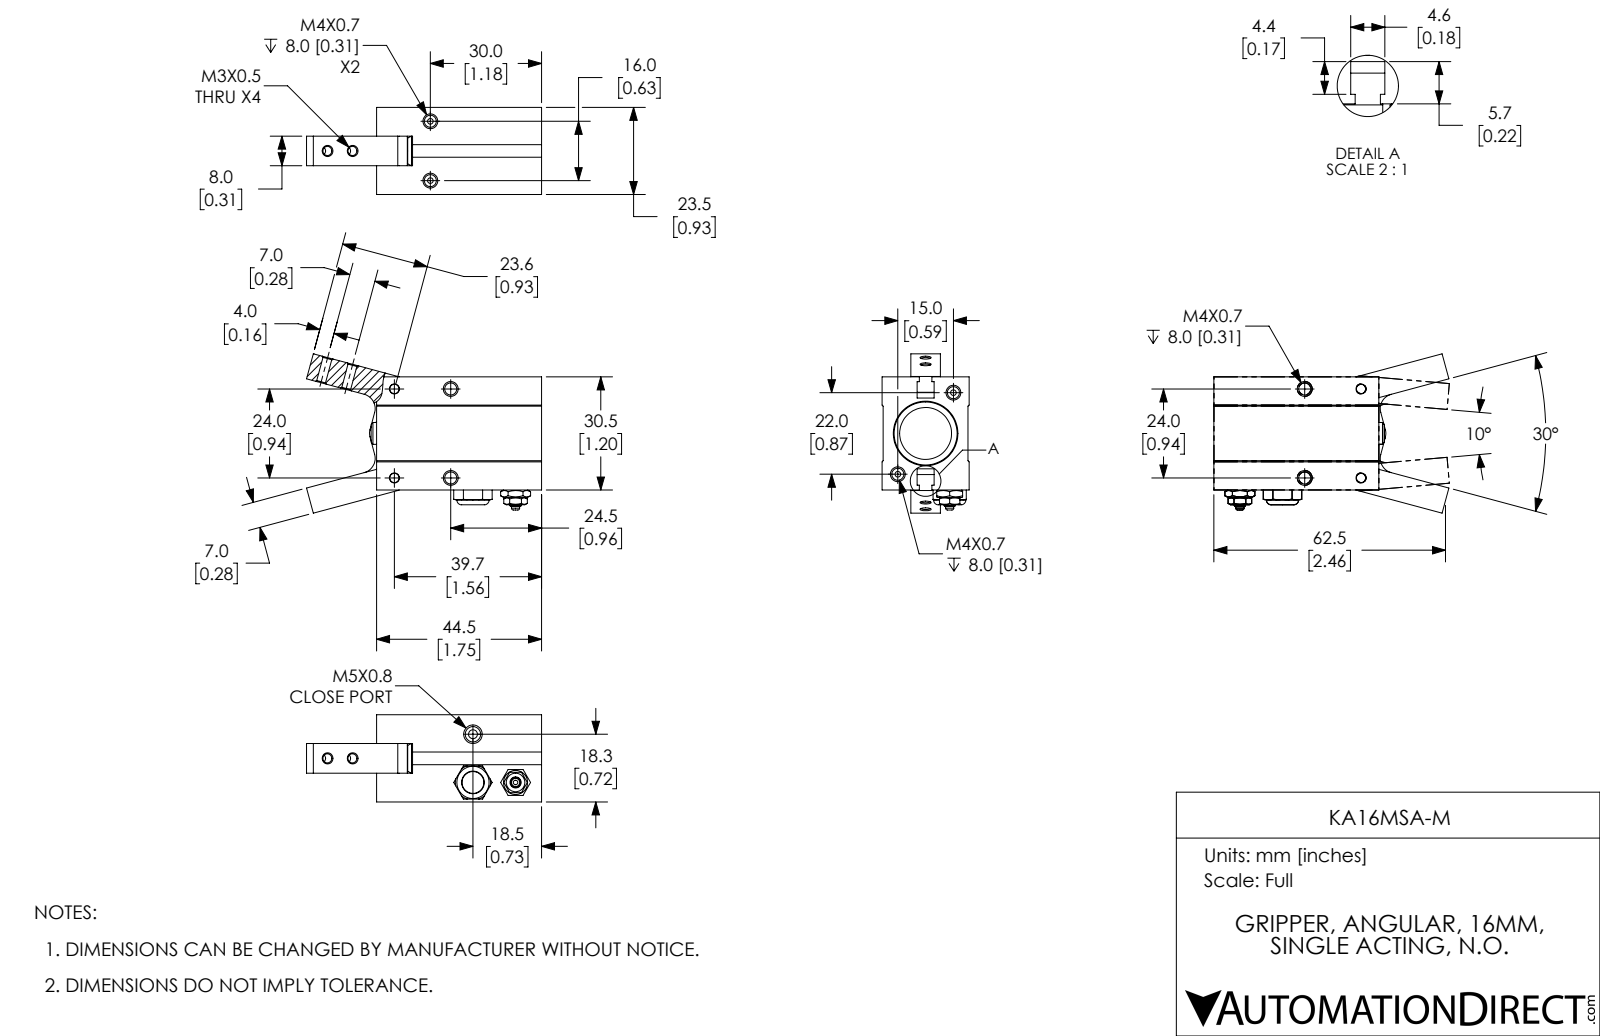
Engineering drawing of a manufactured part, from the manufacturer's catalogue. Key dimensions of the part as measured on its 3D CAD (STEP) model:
Part name (STEP PRODUCT): KA16MSA-M; KA16MSA-M-1; KA16MSA-M-4; KA16MSA-M-3 (+1 more)
STEP written by: SolidWorks 2017 (AUTOMOTIVE_DESIGN)
Units: millimetres
Bodies: 4 solids, 294 faces (114 planar, 92 cylindrical, 88 other)
Overall size (bounding box): 63.4 × 42.98 × 23.5
Volume: 26 988 mm³ · Surface area: 14 659 mm²
Round holes (diameter × count): ⌀3.24 ×6, ⌀2.46 ×4, ⌀2.5 ×2, ⌀4.13 ×2, ⌀4.2 ×2, ⌀2.1 ×1, ⌀8 ×1, ⌀14 ×1, ⌀16 ×1, ⌀17 ×1, ⌀18 ×1
Round bosses / shafts (diameter × count): ⌀7 ×2, ⌀15.9 ×1, ⌀8.7 ×1, ⌀3 ×1, ⌀2.2 ×1
Partial cylindrical surfaces — rounded edges, fillets, slot ends (radius × count): R3.5 ×2, R4 ×2
Main face-to-face distances: 23.2, 7.75, 15.75, 7.45, 15.45, 30.5, 1.7, 23.5, 22.9, 2.3
Hole centre spacings: 7, 11.6, 12.42, 13.31, 15.2, 18.51, 21.97, 24
